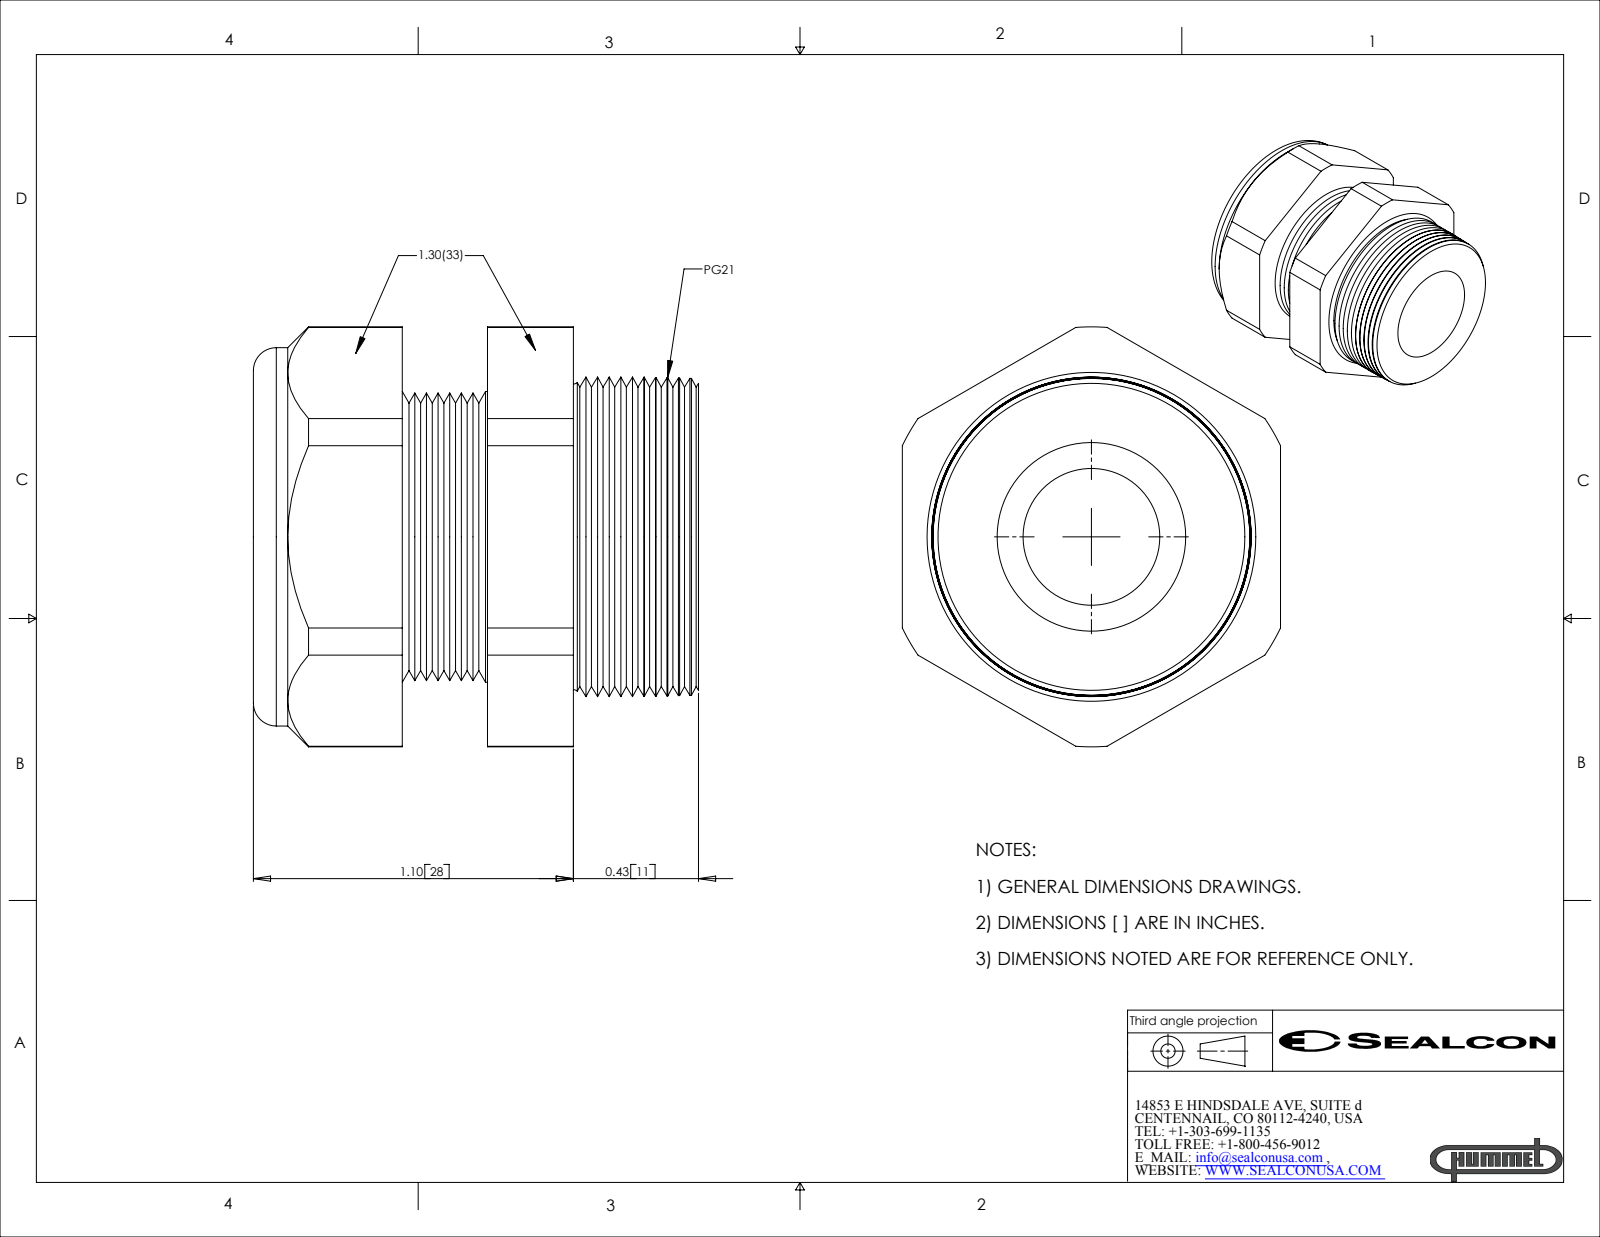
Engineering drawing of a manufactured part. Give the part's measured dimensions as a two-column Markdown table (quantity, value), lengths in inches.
| quantity | value |
| --- | --- |
| part name | CD21BR-GY |
| STEP written by | SolidWorks 2007 (CONFIG_CONTROL_DESIGN) |
| units | inches |
| bodies | 2 solids, 142 faces (20 planar, 24 cylindrical, 98 other) |
| overall size | 1.53 × 1.443 × 1.3 |
| volume | 1.407 in³ |
| surface area | 17.71 in² |
| round holes (diameter × count) | 0.47 × 1, 0.888 × 1 |
| round bosses / shafts (diameter × count) | 1.3 × 1, 0.999 × 1 |
| partial cylindrical surfaces (radius × count) | 0.721 × 1 |
| main face-to-face distances | 1.3, 0.293, 1.018, 0.725, 0.588, 0.295, 0.43, 0.512, 0.805, 1.1 |
